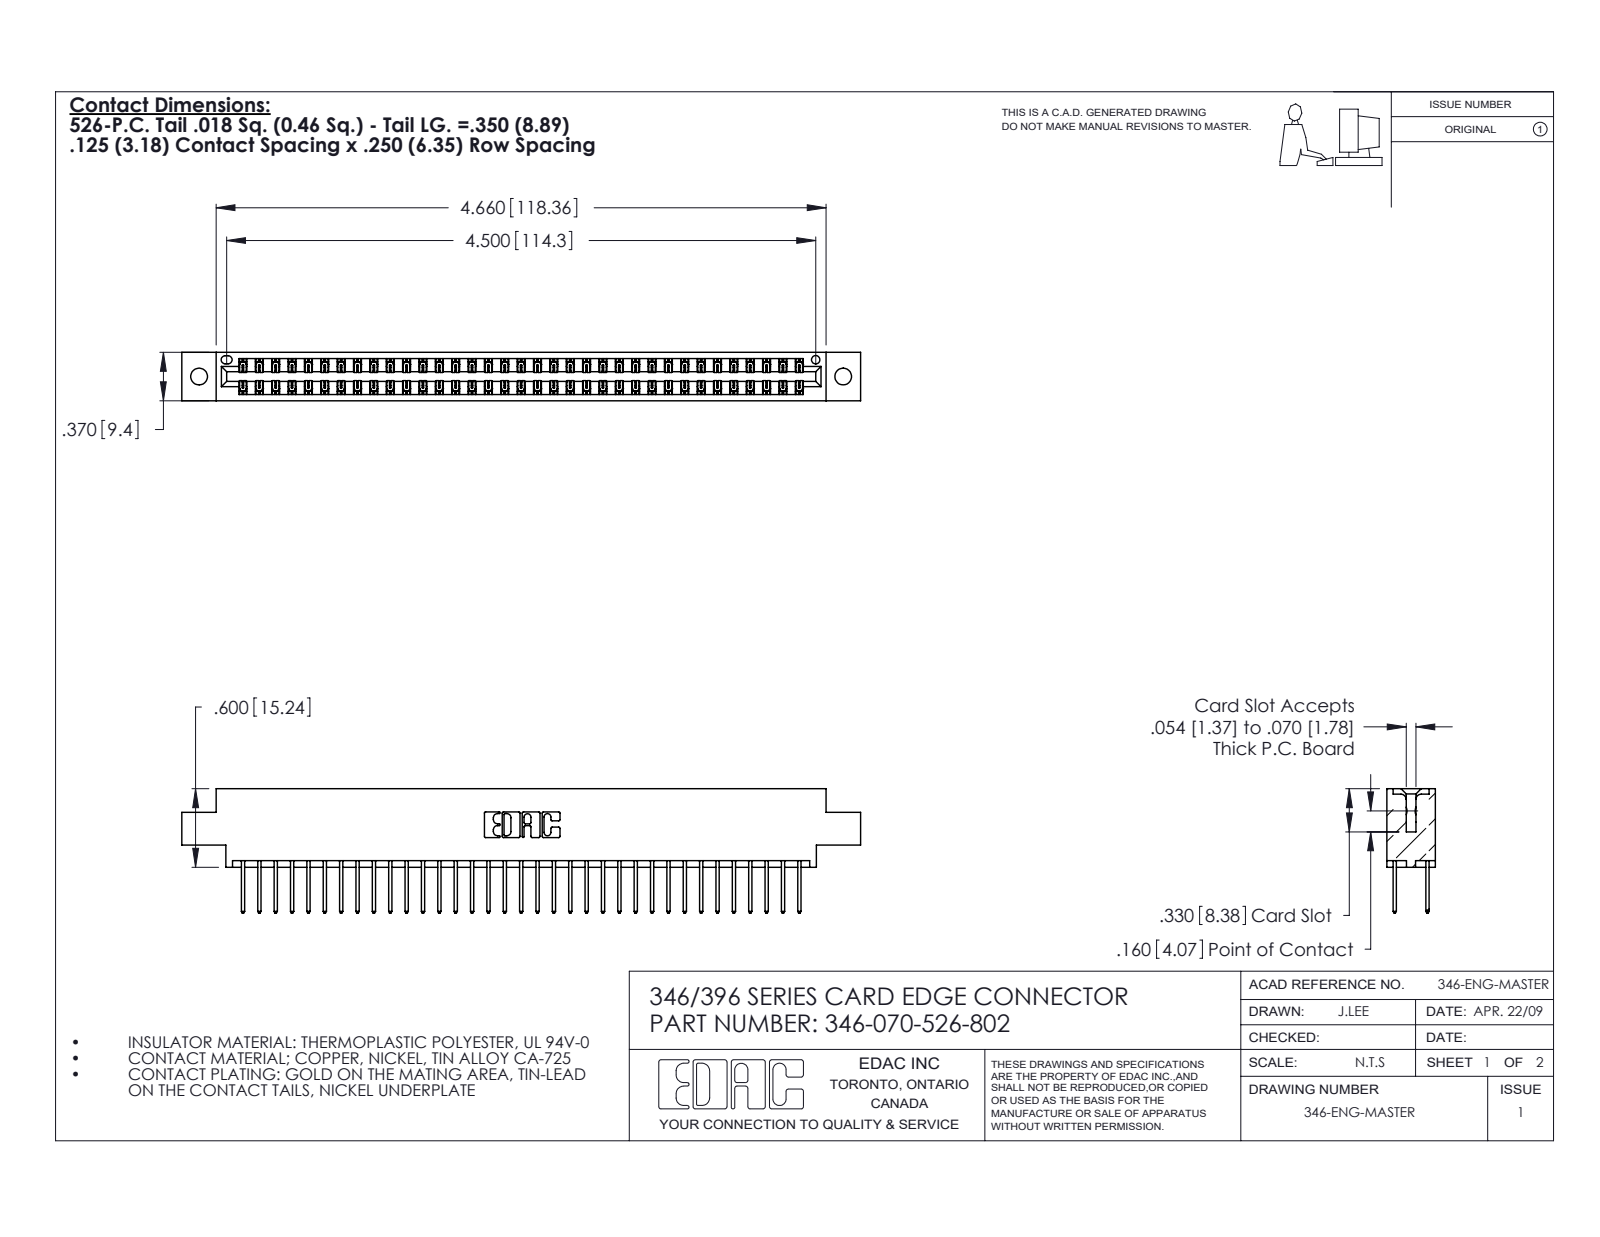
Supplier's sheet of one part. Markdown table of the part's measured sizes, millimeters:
| quantity | value |
| --- | --- |
| part name | 346-070-526-802; 345-292-001_345-293-126; 346 Part_0.170 Offset - 0.128 Dia |
| STEP written by | SolidWorks 2020 (CONFIG_CONTROL_DESIGN) |
| units | millimeters |
| bodies | 71 solids, 3766 faces (2530 planar, 1236 cylindrical, 0 other) |
| overall size | 131.7 × 24.1 × 9.4 |
| volume | 12 700 mm³ |
| surface area | 17 790 mm² |
| round holes (diameter × count) | 3.3 × 2, 1.6 × 1 |
| partial cylindrical surfaces (radius × count) | 0.2 × 105, 0.3 × 70, 0.3 × 22, 0.2 × 6, 0.8 × 6, 0.7 × 3, 0.4 × 2, 0.6 × 2 |
| main face-to-face distances | 1.2, 8.2, 6.4, 9.4, 1.8, 7.6, 0.6, 7, 3.8, 5.6 |
| hole center spacings | 6.2, 119.7, 125 |
